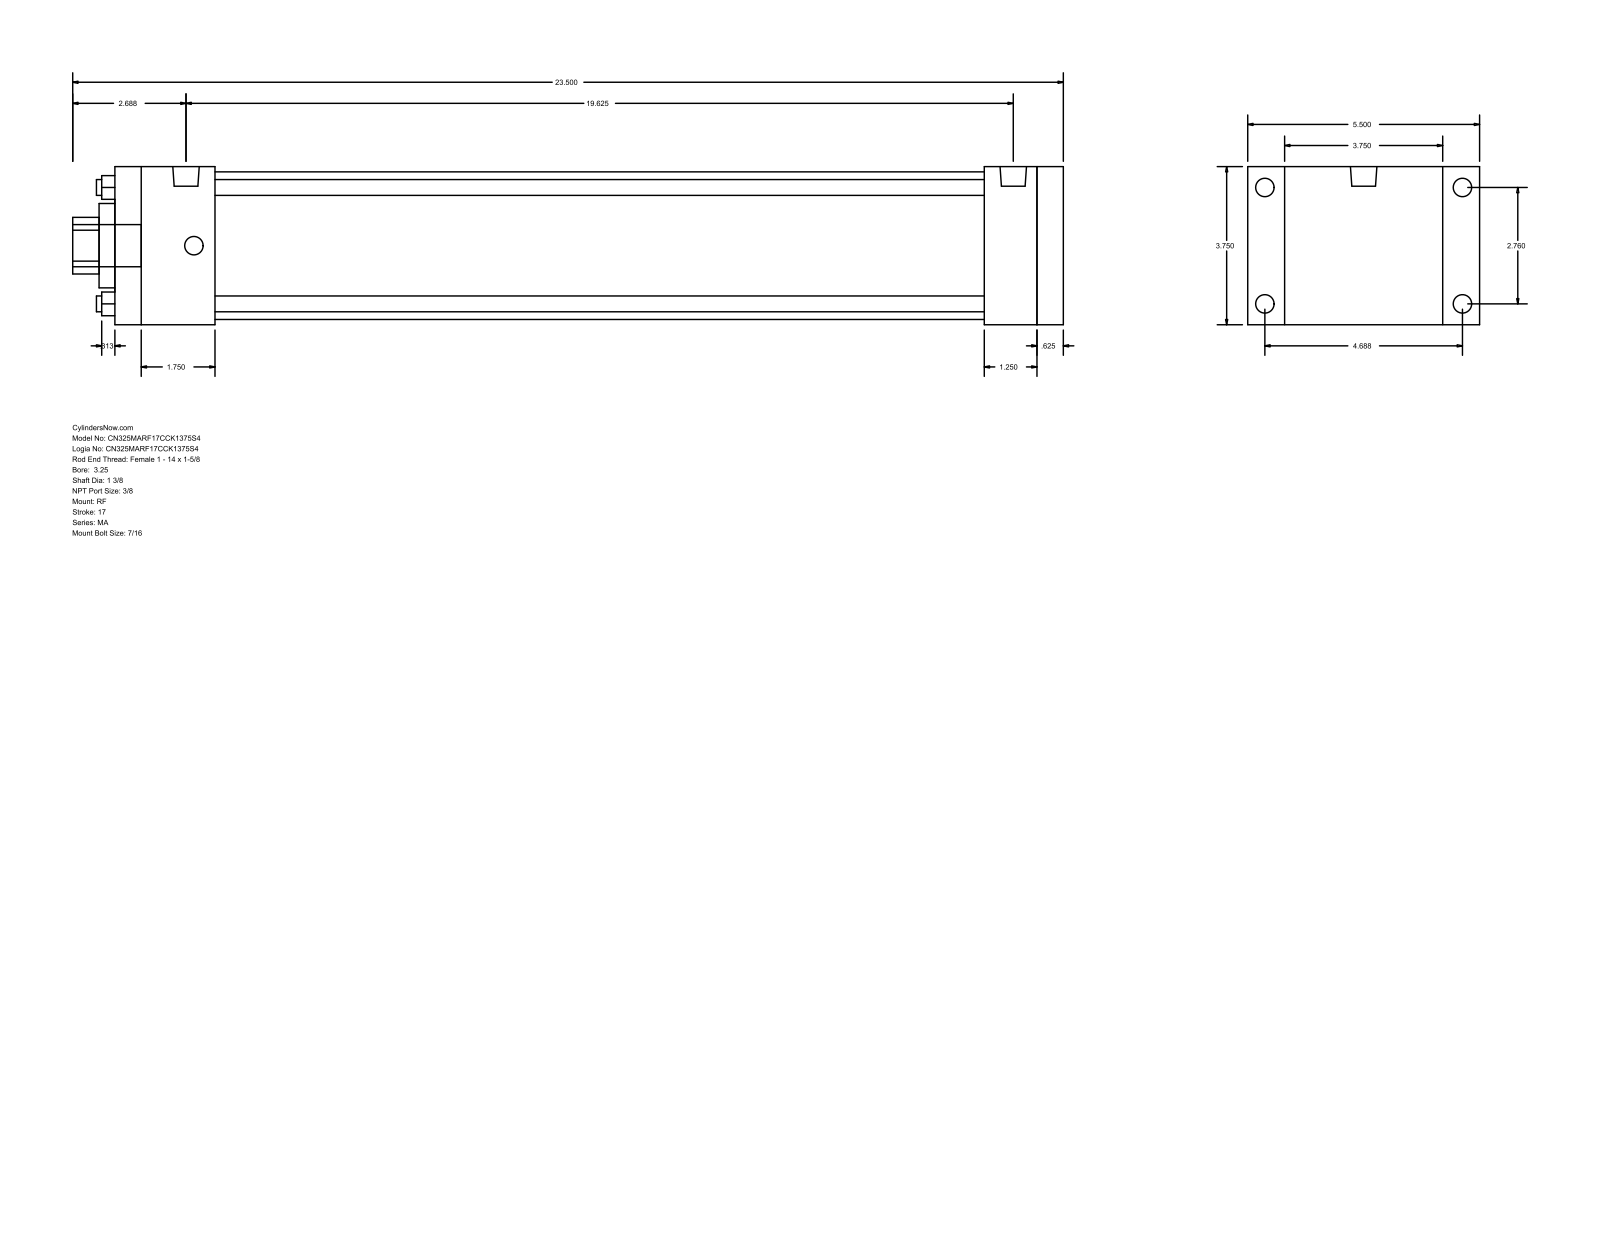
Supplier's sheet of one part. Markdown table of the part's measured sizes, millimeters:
| quantity | value |
| --- | --- |
| part name | MA_RF__0325_1.375 |
| STEP written by | GSSL Pune (CONFIG_CONTROL_DESIGN) |
| units | millimeters |
| bodies | 0 solids, 92 faces (64 planar, 28 cylindrical, 0 other) |
| overall size | 596.9 × 139.7 × 95.25 |
| round holes (diameter × count) | 9.53 × 4, 34.92 × 1, 50.8 × 1, 88.9 × 1 |
| round bosses / shafts (diameter × count) | 11.11 × 8, 15.93 × 2, 25.4 × 1 |
| partial cylindrical surfaces (radius × count) | 17.06 × 1 |
| main face-to-face distances | 95.24, 571.5, 15.88, 555.62, 22.23, 117.47, 523.87, 31.75, 47.63, 60.32 |
| hole center spacings | 49.57, 70.1, 99.14 |
